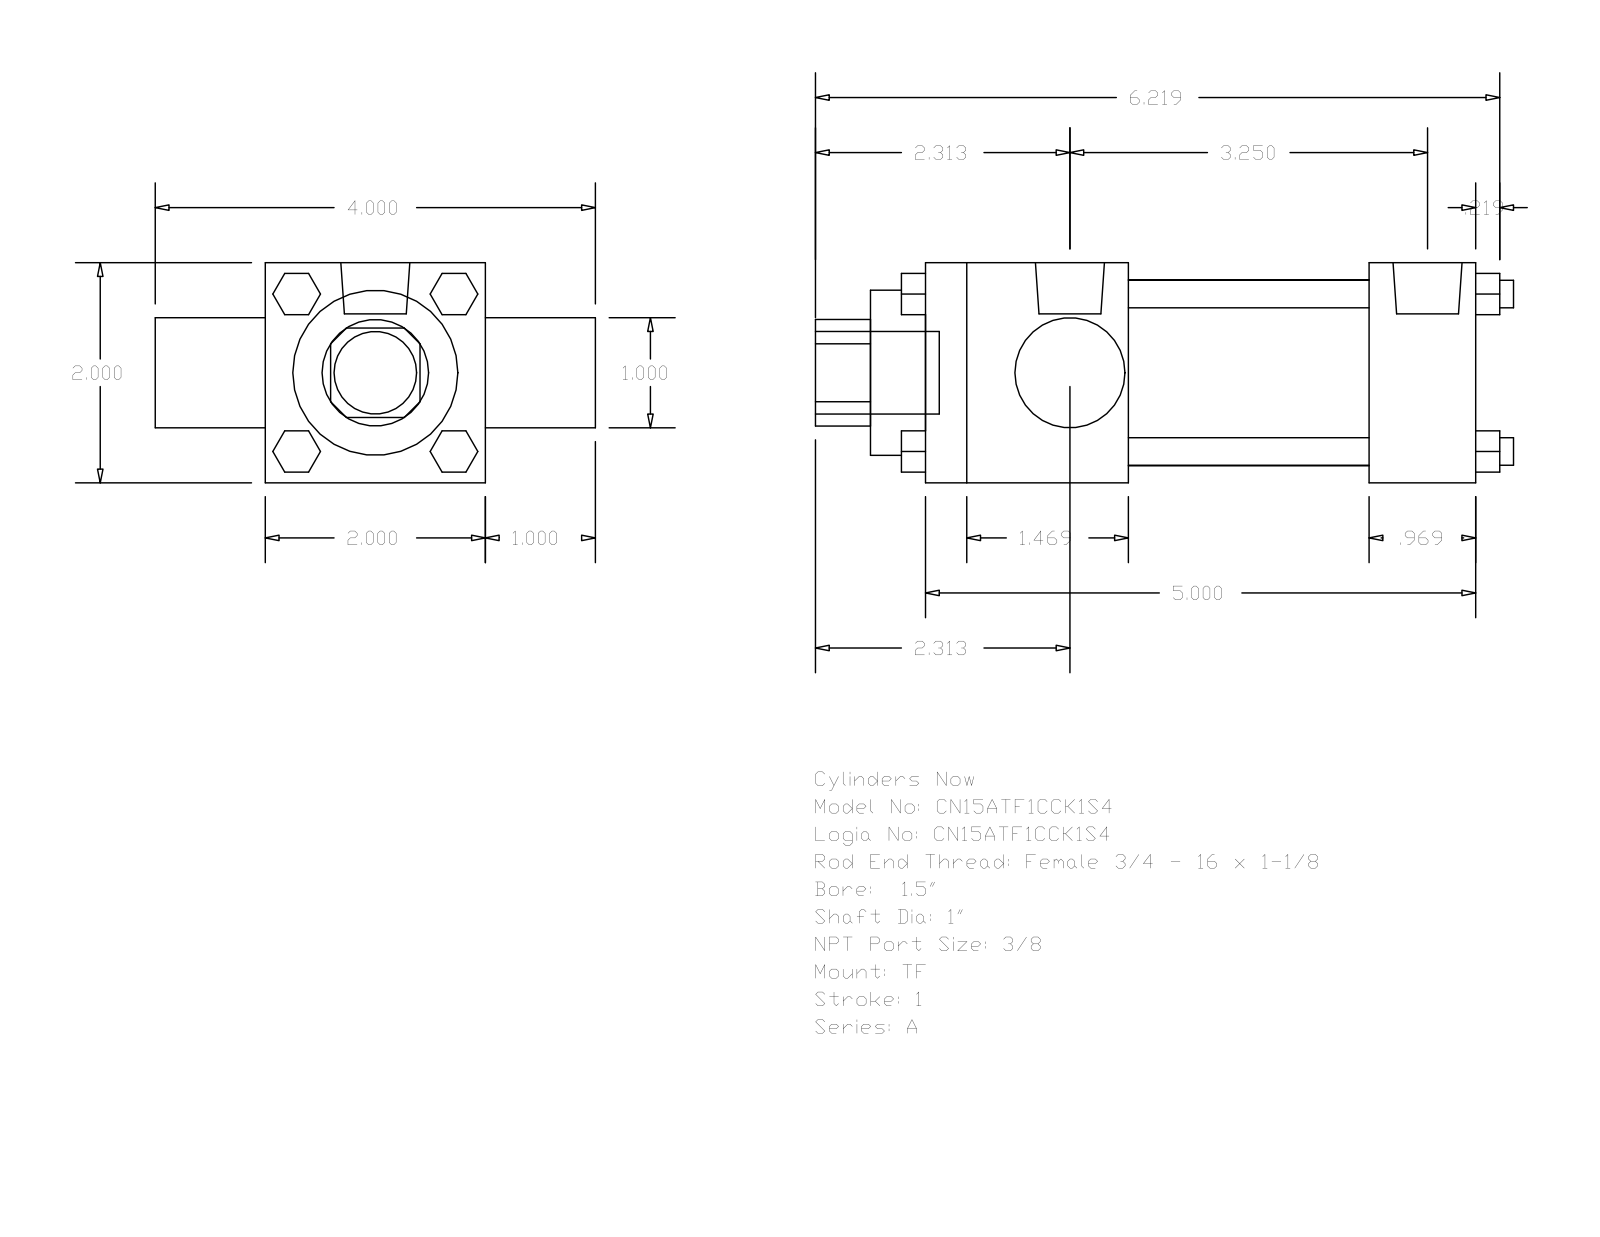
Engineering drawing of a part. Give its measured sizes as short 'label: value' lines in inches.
name: A_TF__0150_1
written by: GSSL Pune (CONFIG_CONTROL_DESIGN)
unit: in
bodies: 0 solids, 120 faces (92 planar, 28 cylindrical, 0 other)
size: 6.344 × 4 × 2
holes: 2× ⌀1, 1× ⌀1.5, 1× ⌀1.69
bosses: 4× ⌀0.25, 3× ⌀0.219, 2× ⌀0.627, 1× ⌀0.75
rounds: 1× R0.484
face distances: 2, 1, 5, 3, 1.844, 4.031, 2.187, 3.156, 0.969, 0.5
